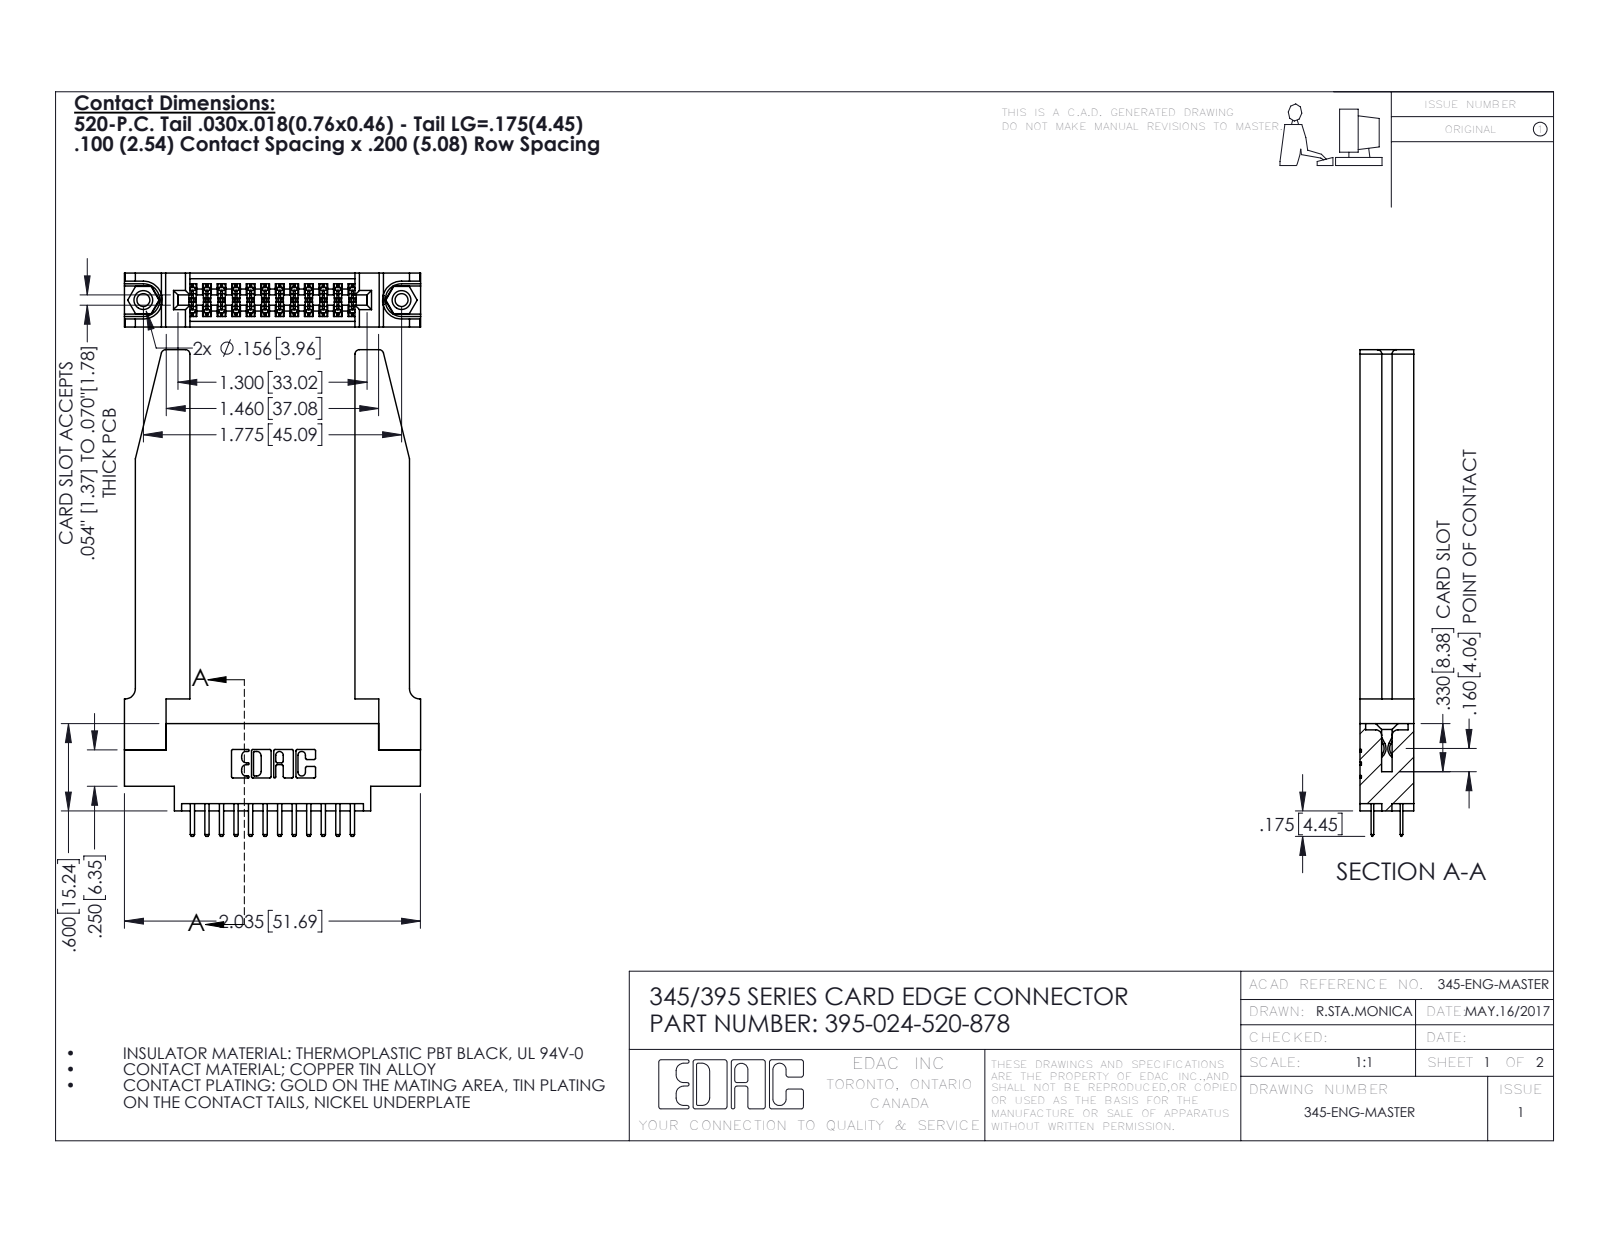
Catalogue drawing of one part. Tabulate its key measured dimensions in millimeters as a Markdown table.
| quantity | value |
| --- | --- |
| part name | 345-220-078_345-220-078; 395-024-520-878; 345 Part_0.170 Offset - 0.156 Dia-TH; 345-250-001_345-250-001-102 (+1 more) |
| STEP written by | SolidWorks 2016 (CONFIG_CONTROL_DESIGN) |
| units | millimeters |
| bodies | 29 solids, 1660 faces (1066 planar, 542 cylindrical, 52 other) |
| overall size | 85 × 51.7 × 9.4 |
| volume | 12 400 mm³ |
| surface area | 13 210 mm² |
| round holes (diameter × count) | 2.3 × 2, 3.2 × 2, 4 × 2, 1.6 × 1 |
| round bosses / shafts (diameter × count) | 3.9 × 2 |
| partial cylindrical surfaces (radius × count) | 0.2 × 36, 0.3 × 28, 0.3 × 22, 0.8 × 8, 0.2 × 6, 0.8 × 6, 0.7 × 3, 0.4 × 2 |
| main face-to-face distances | 9.4, 1.8, 7.6, 5.1, 3.8, 5.6, 2, 3.8, 28.8, 3.1 |
| hole center spacings | 6.9, 39.2, 45.1 |
